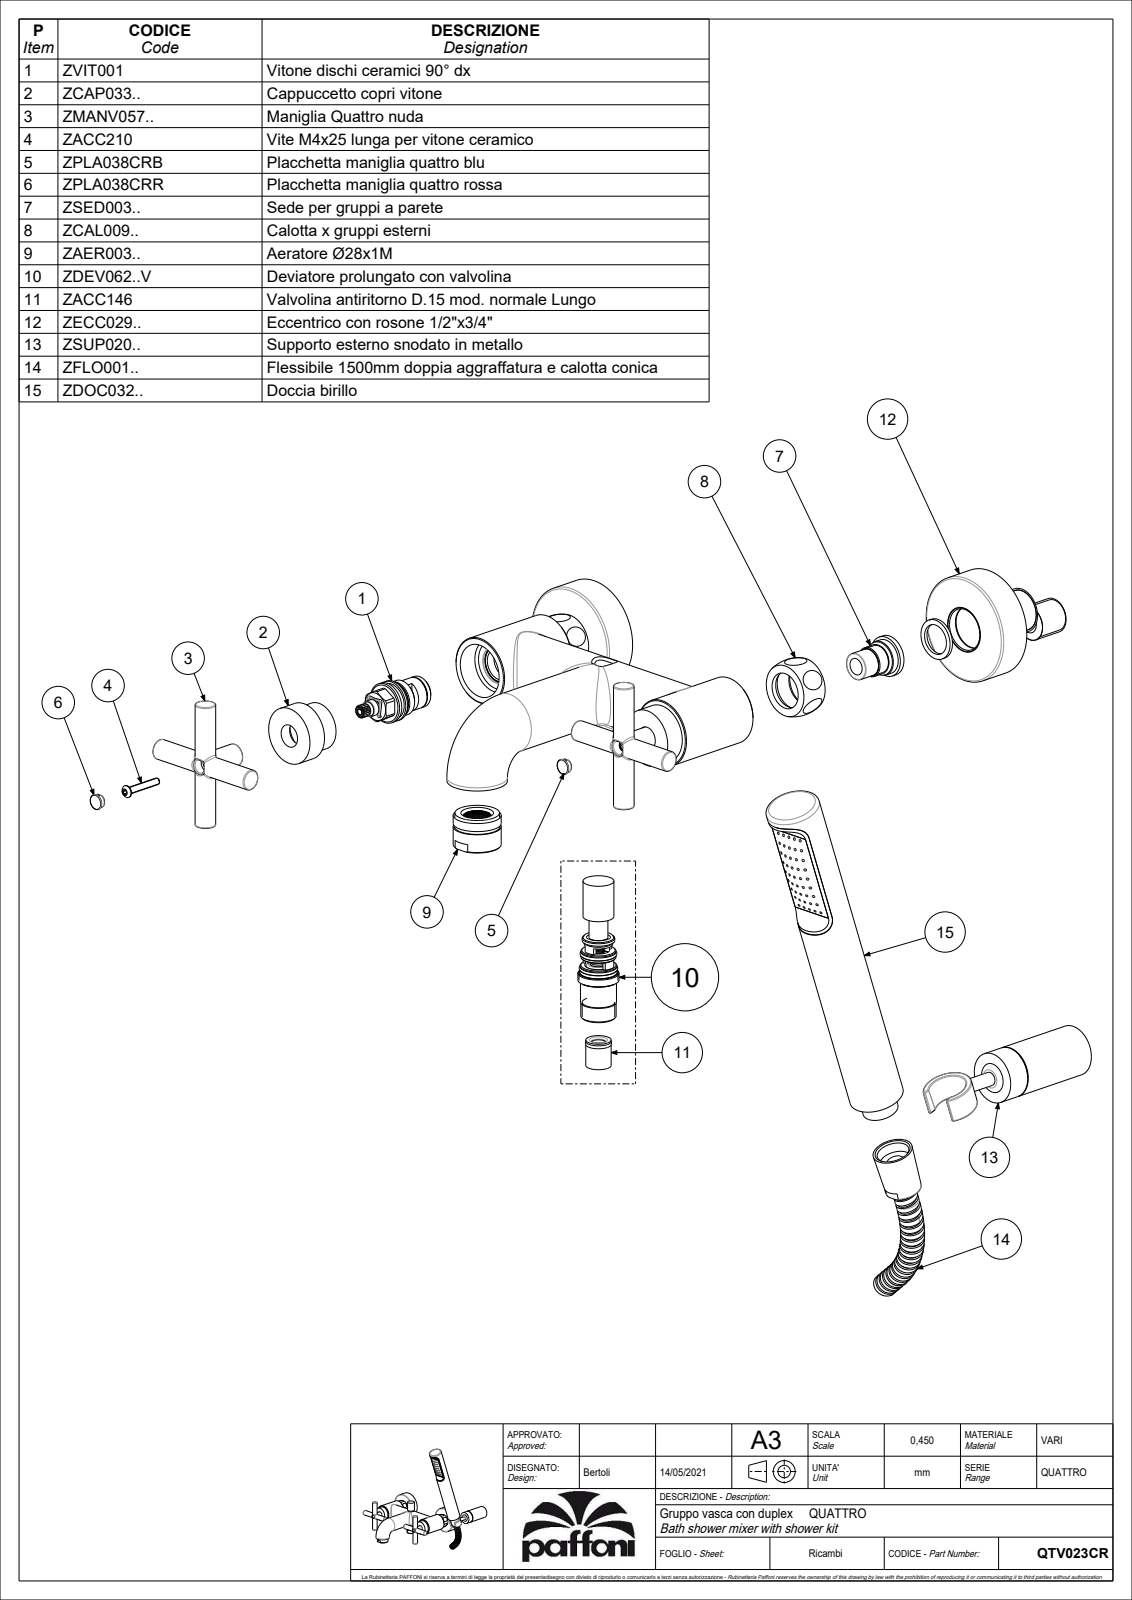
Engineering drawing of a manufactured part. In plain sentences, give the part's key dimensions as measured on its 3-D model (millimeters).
The part is named "QTV023CR". Its 3-D file was written by "CREO PARAMETRIC BY PTC INC, 2020044 (CONFIG_CONTROL_DESIGN)". It is 7 solids with 2828 faces: 1978 planar, 461 cylindrical and 389 other. Overall it measures 328.5 by 312.56 by 191.39 millimeters. Its volume is 407 856 cubic millimeters and its surface area 218 990 square millimeters. Round holes: 45 of diameter 1.5, 3 of diameter 3.3, 3 of diameter 10, 3 of diameter 18, 3 of diameter 25, 2 of diameter 4.5, 2 of diameter 7, 2 of diameter 8, 2 of diameter 8.8, 2 of diameter 9.5, 2 of diameter 13.5, 2 of diameter 16.3. Round bosses or shafts: 3 of diameter 24, 3 of diameter 20.5, 3 of diameter 12, 2 of diameter 63.5, 2 of diameter 40, 2 of diameter 35.3, 2 of diameter 34, 2 of diameter 30. Partial cylindrical surfaces (rounded edges, fillets, slot ends): 34 of radius 0.1, 14 of radius 0.5, 4 of radius 1, 3 of radius 10, 2 of radius 3, 2 of radius 7.8, 2 of radius 9.4, 2 of radius 9.8. The main face-to-face distances are 0.6, 67.8, 56.8, 12, 11, 18.5, 19.1, 1, 37.5, 86.9. The hole center spacings are 7.91, 13.76, 6.5, 4.5, 11.1, 13, 26.39, 39.26.
